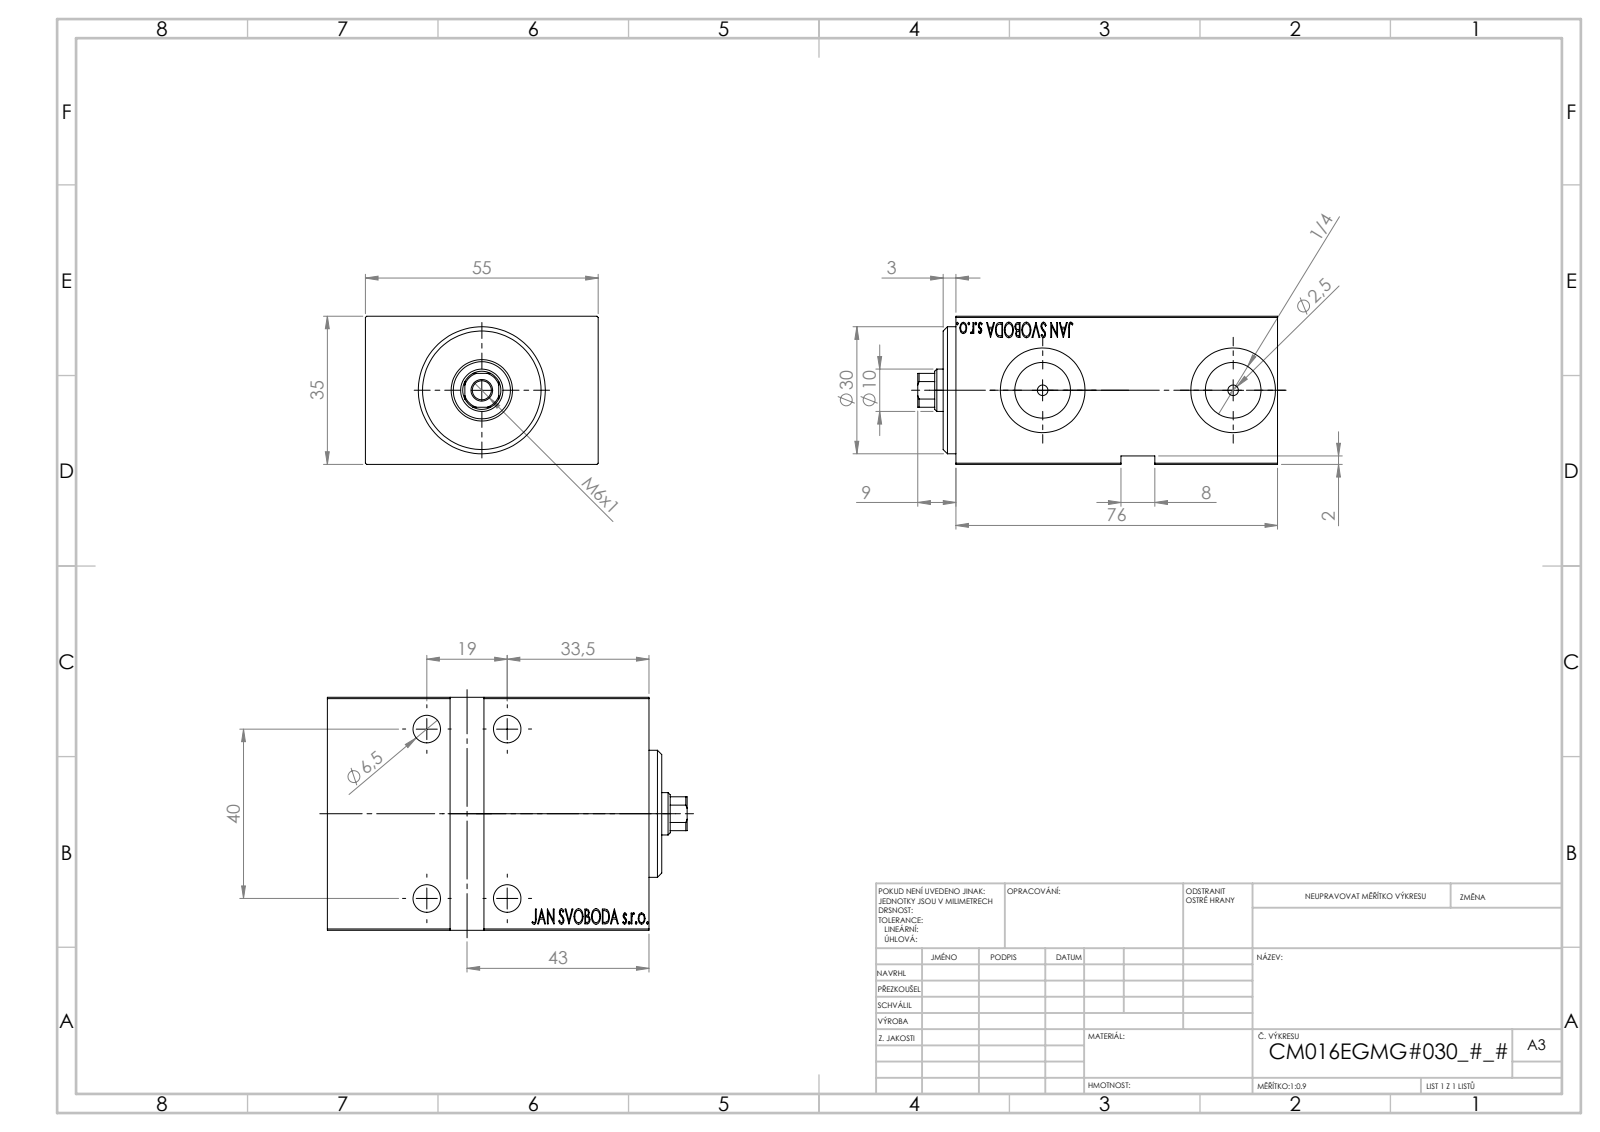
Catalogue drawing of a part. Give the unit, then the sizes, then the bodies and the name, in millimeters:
Units: millimetres
Overall size (bounding box): 85 × 55 × 35
Round holes (diameter × count): ⌀6.5 ×4, ⌀10.5 ×4, ⌀2.5 ×2, ⌀13.16 ×2, ⌀20 ×2, ⌀4.5 ×1, ⌀10 ×1, ⌀13.5 ×1, ⌀14.5 ×1, ⌀16 ×1, ⌀18 ×1, ⌀25 ×1
Round bosses / shafts (diameter × count): ⌀30 ×1
Partial cylindrical surfaces — rounded edges, fillets, slot ends (radius × count): R4.5 ×1
Main face-to-face distances: 35, 55, 76, 5, 71, 8, 42, 3, 79, 2
Hole centre spacings: 19, 40, 44.28, 45
Volume: 132 551 mm³ · Surface area: 32 406 mm²
Bodies: 3 solids, 862 faces (412 planar, 56 cylindrical, 394 other)
Part name (STEP PRODUCT): V450CM_VC_B; V450CM_E_Body; V450CM_E_VCP
STEP written by: SolidWorks 2019 (CONFIG_CONTROL_DESIGN)
